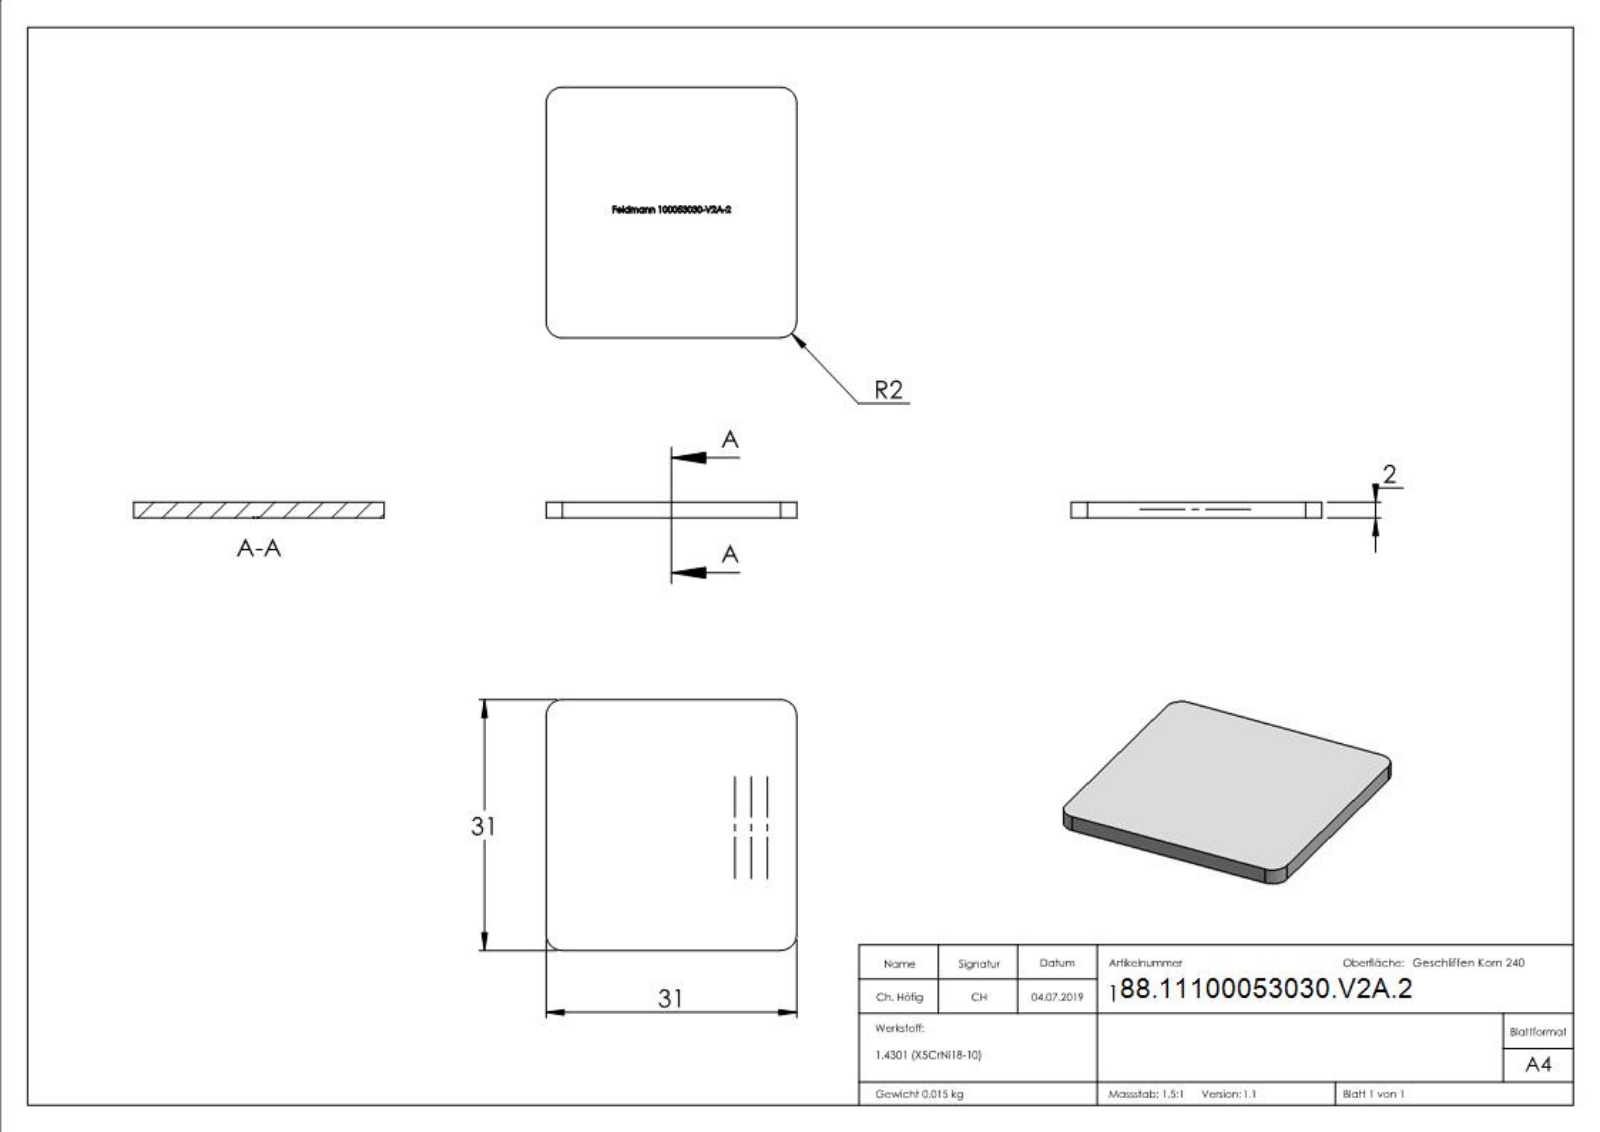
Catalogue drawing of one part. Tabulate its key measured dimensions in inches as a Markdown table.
| quantity | value |
| --- | --- |
| part name | 100053030-V2A-2 |
| STEP written by | SolidWorks 2015 (CONFIG_CONTROL_DESIGN) |
| units | inches |
| bodies | 1 solid, 293 faces (148 planar, 4 cylindrical, 141 other) |
| overall size | 1.22 × 1.22 × 0.079 |
| volume | 0.117 in³ |
| surface area | 3.354 in² |
| partial cylindrical surfaces (radius × count) | 0.079 × 4 |
| main face-to-face distances | 0.079, 1.22, 0.075, 0.61, 0.07, 0.073, 0.03, 0.017, 0.039, 0.109 |
